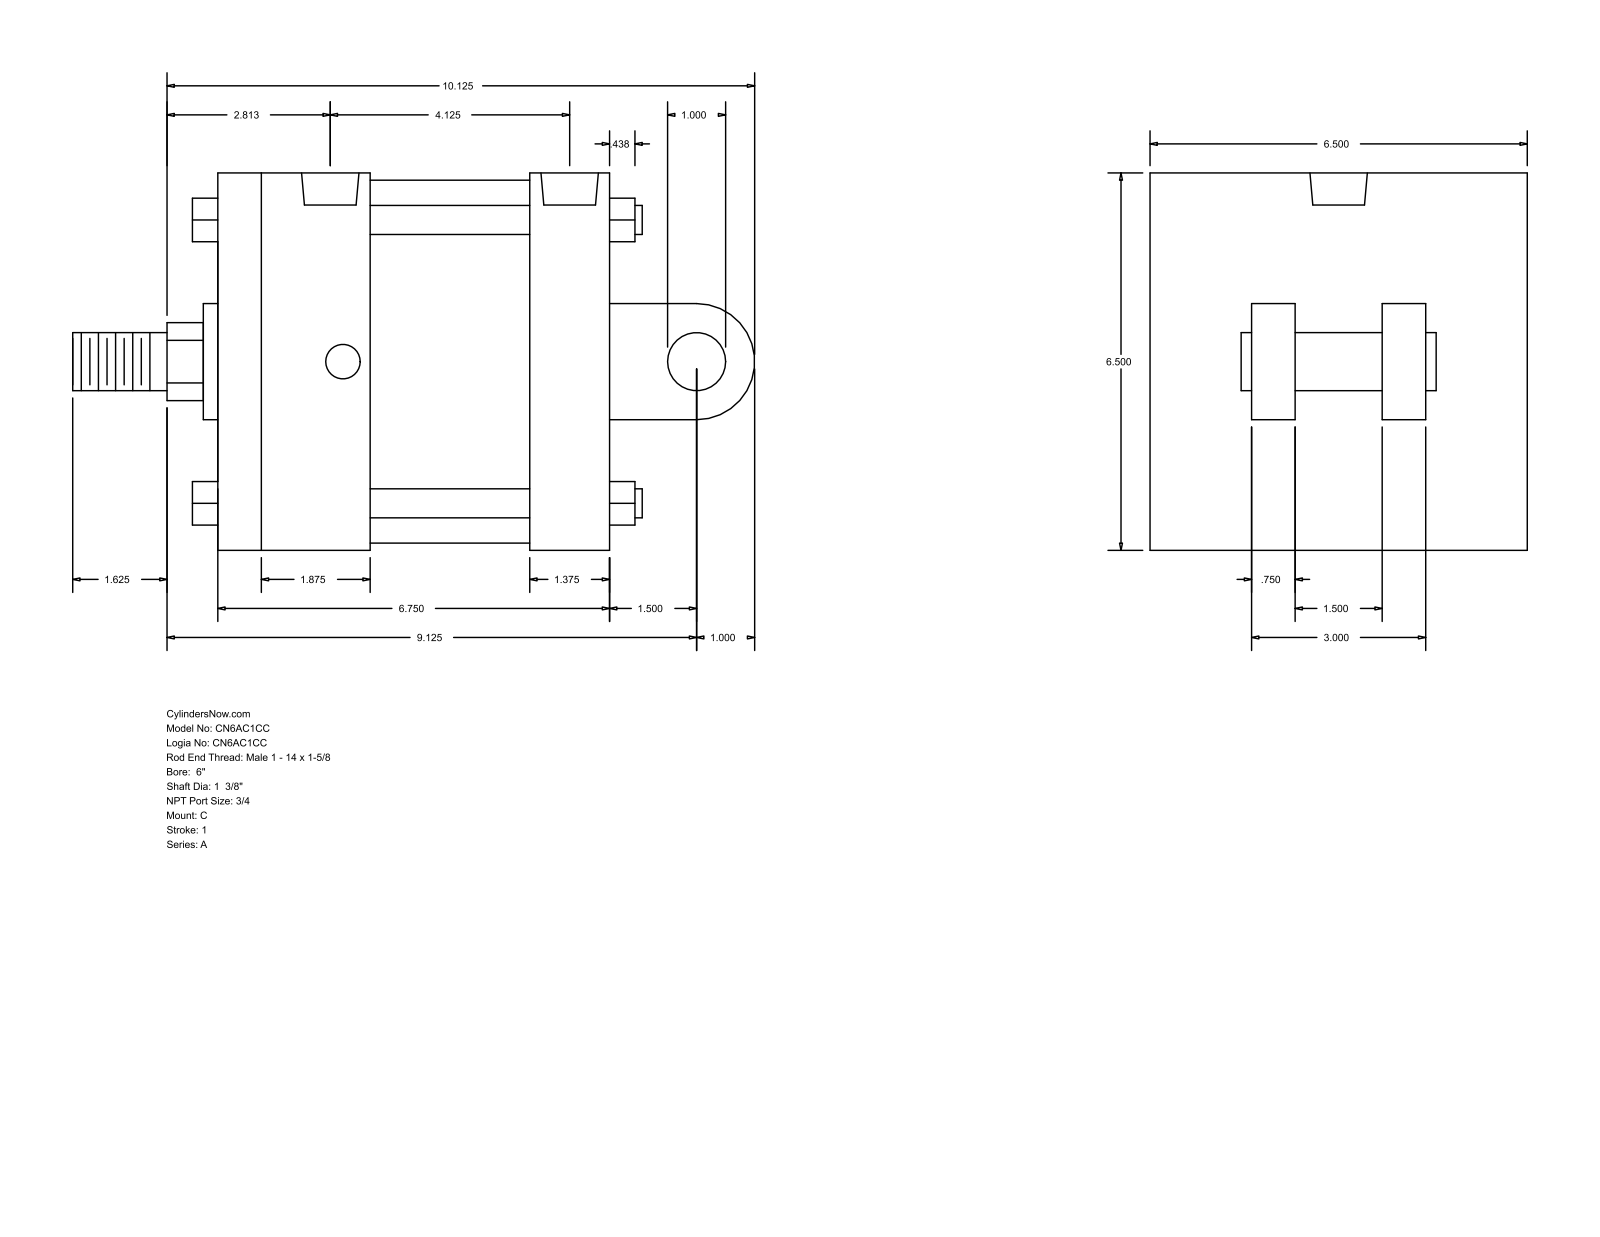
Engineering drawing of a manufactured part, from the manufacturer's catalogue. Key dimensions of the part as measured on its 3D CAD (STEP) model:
Part name (STEP PRODUCT): A_C__0600_1.375
STEP written by: GSSL Pune (CONFIG_CONTROL_DESIGN)
Units: millimetres
Bodies: 0 solids, 135 faces (102 planar, 33 cylindrical, 0 other)
Overall size (bounding box): 298.45 × 165.1 × 165.1
Round holes (diameter × count): ⌀15.08 ×4, ⌀25.12 ×2
Round bosses / shafts (diameter × count): ⌀12.7 ×4, ⌀25.4 ×2, ⌀158.75 ×1, ⌀50.8 ×1, ⌀34.92 ×1
Partial cylindrical surfaces — rounded edges, fillets, slot ends (radius × count): R17.06 ×1, R25.4 ×1
Main face-to-face distances: 165.1, 171.45, 57.15, 19.05, 66.67, 104.78, 136.52, 69.85, 34.93, 63.5
Hole centre spacings: 5.56, 93.65, 99.21, 104.77
